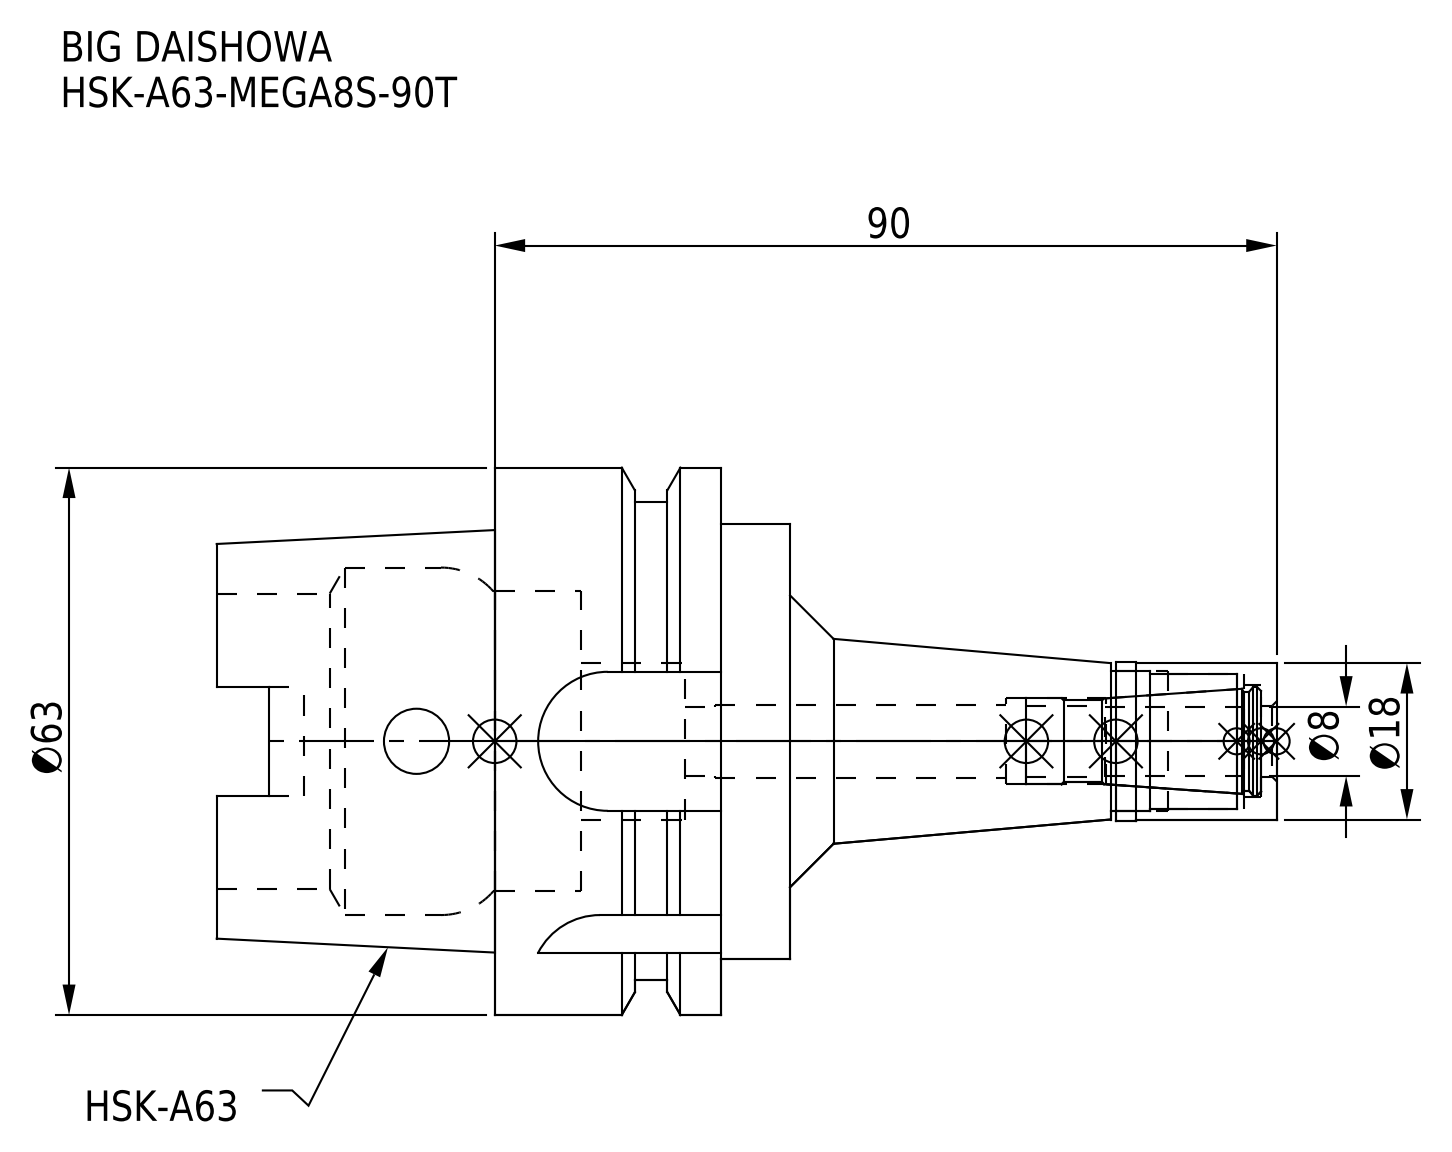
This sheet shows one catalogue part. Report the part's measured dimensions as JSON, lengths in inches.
{"part_name": "HSK-A63-MEGA8S-90T-080.stp; DXF_TEMP_ASSY_ASM_4_ASM.stp; HA63MS08090T-080_ASM.stp; MGN8S_1.stp (+3 more)", "step_written_by": "SolidWorks 2019 (CONFIG_CONTROL_DESIGN)", "units": "inches", "bodies": {"solids": 2, "faces": 122, "planar": 47, "cylindrical": 53, "other": 22}, "overall_size": [4.803, 2.48, 2.48], "volume_in3": 6.814, "surface_area_in2": 47.15, "round_holes": [[0.295, 1], [0.315, 1], [0.323, 1], [0.331, 1], [0.39, 1], [0.508, 1], [0.614, 1], [0.634, 1], [0.709, 1], [1.339, 1], [1.358, 1], [1.575, 1]], "round_bosses_or_shafts": [[2.48, 1], [2.165, 1], [1.969, 1], [0.72, 1]], "partial_cylinders_radius": [[0.113, 4], [0.315, 4]], "face_to_face_distances": [1.339, 1.024, 0.315, 0.947, 0.632, 0.392, 2.598, 2.283, 1.652, 1.26]}
